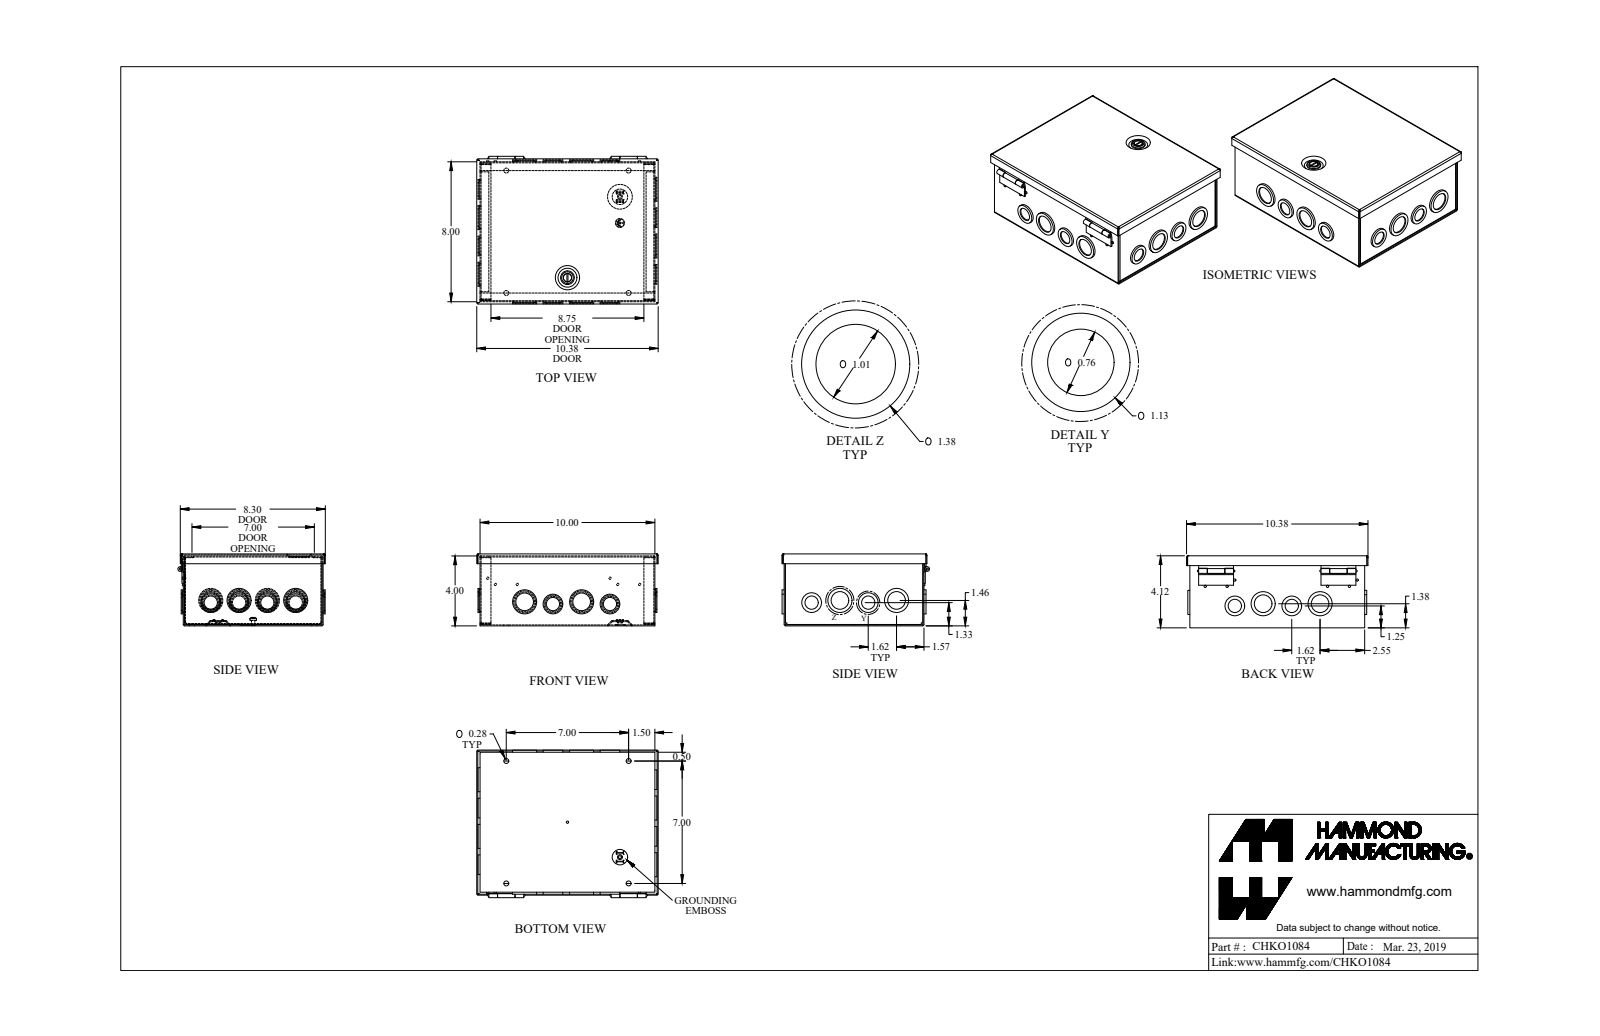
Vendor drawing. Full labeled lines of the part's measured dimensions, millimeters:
Part name (STEP PRODUCT): CHKO1084_Default
STEP written by: SolidWorks 2019 (CONFIG_CONTROL_DESIGN)
Units: millimetres
Bodies: 12 solids, 679 faces (336 planar, 300 cylindrical, 43 other)
Overall size (bounding box): 263.7 × 214.5 × 104.6
Volume: 356 100 mm³ · Surface area: 493 700 mm²
Round holes (diameter × count): ⌀25.7 ×12, ⌀19.3 ×6, ⌀32 ×6, ⌀7.1 ×4, ⌀3.2 ×1, ⌀4.3 ×1, ⌀8.1 ×1, ⌀12.1 ×1, ⌀12.7 ×1
Round bosses / shafts (diameter × count): ⌀3.3 ×8, ⌀28.6 ×6, ⌀28.6 ×6, ⌀34.9 ×4, ⌀22.2 ×4, ⌀22.2 ×4, ⌀34.9 ×2, ⌀20 ×1
Partial cylindrical surfaces — rounded edges, fillets, slot ends (radius × count): R0.7 ×16, R2.2 ×16, R1.4 ×8, R0.3 ×4, R2.5 ×4, R0.9 ×2, R2 ×2, R6.4 ×2
Main face-to-face distances: 1.4, 103.1, 104.6, 101.7, 201.8, 252.6, 203.2, 200.3, 254, 100.2
Hole centre spacings: 41.3, 3.2, 41.1, 82.3, 82.3, 177.8, 41.1, 41.2
